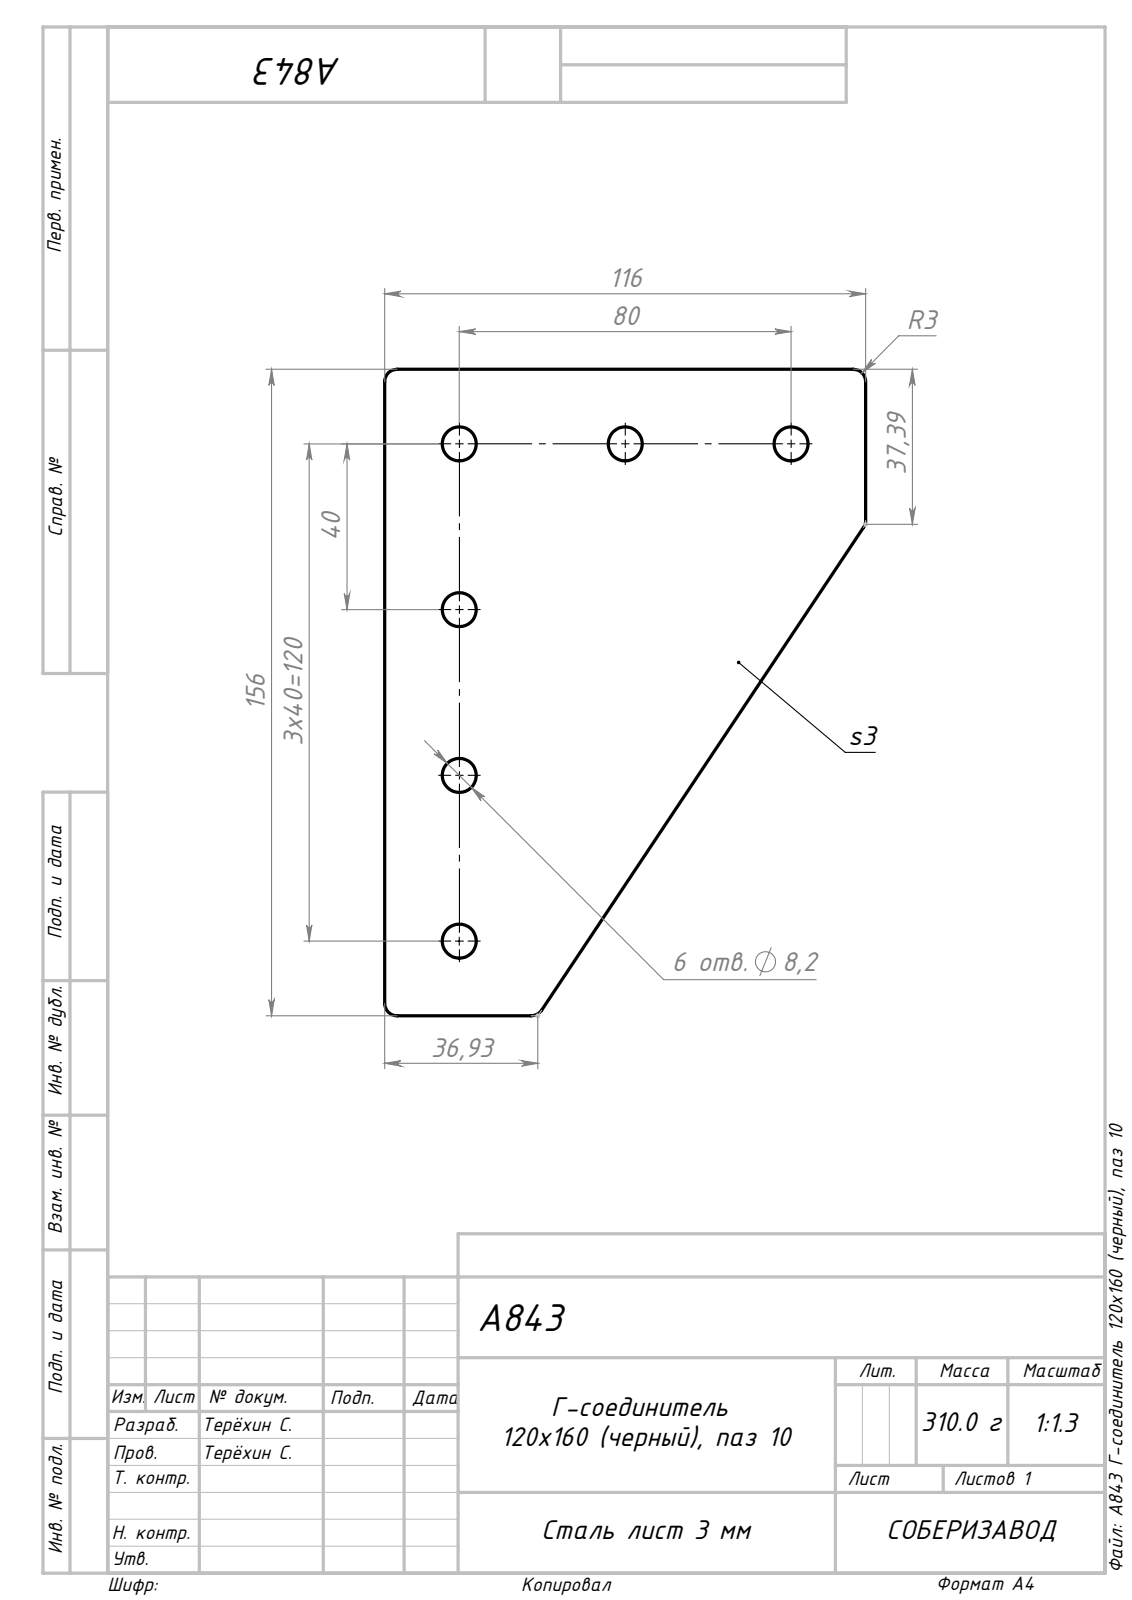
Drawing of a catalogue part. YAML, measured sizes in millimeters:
part_name: "A843 Г-соединитель 120х160 (черный), паз 10_00; Сборка1"
step_written_by: "SolidWorks 2024 (AUTOMOTIVE_DESIGN)"
units: millimeters
bodies: {solids: 1, faces: 24, planar: 7, cylindrical: 17, other: 0}
overall_size: [156, 116, 3]
volume: 39251
surface_area: 28085
round_holes:
  - {diameter: 8.2, count: 6}
partial_cylinders:
  - {radius: 3, count: 5}
face_to_face_distances: [3, 116, 156]
hole_center_spacings: [40, 80, 89.44, 56.57, 113.14, 120, 126.49, 144.22]
